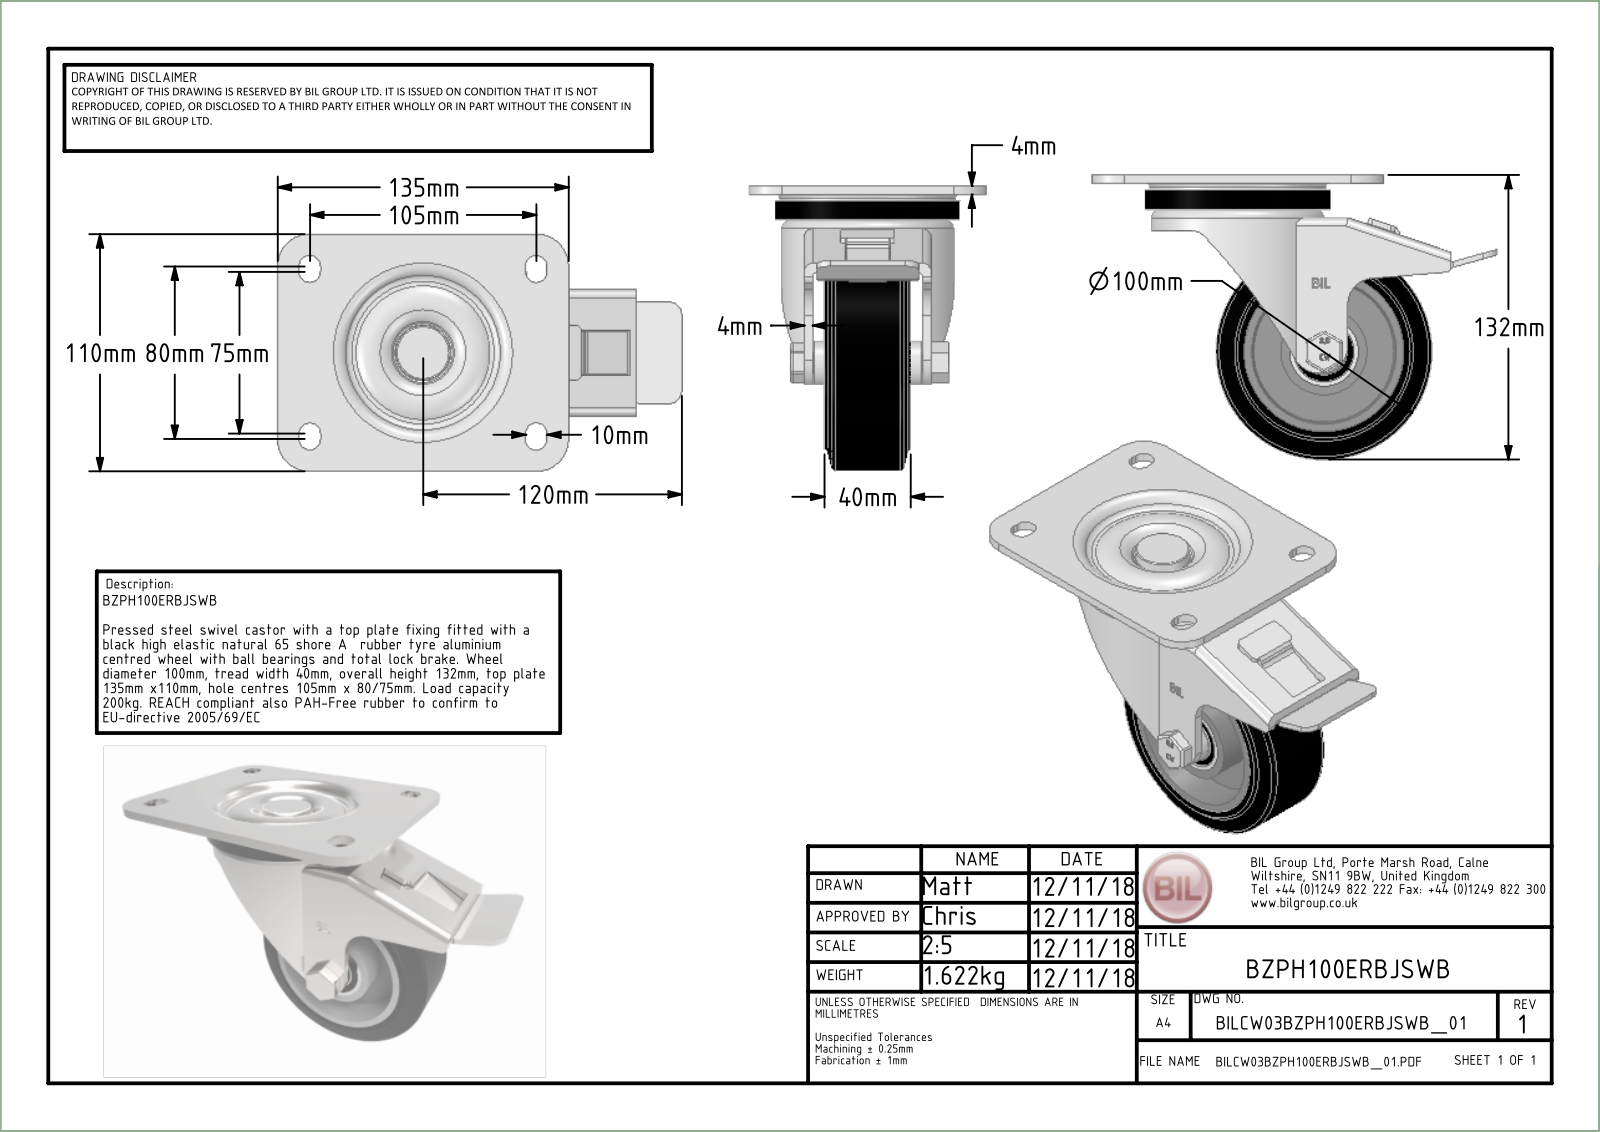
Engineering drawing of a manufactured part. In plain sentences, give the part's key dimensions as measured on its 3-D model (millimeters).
The part is named "BZPH100ERBJSWB v3; BZPH100ASSWB v1; ZINC PLATED, PRESSED STEEL TOP PLATE; ZINC PLATED, PRESSED STEEL FORKS (+8 more)". Its 3-D file was written by "Autodesk Translation Framework v14.4.0.0 (AUTOMOTIVE_DESIGN)". It is 43 solids with 1357 faces: 678 planar, 256 cylindrical and 423 other. Overall it measures 187.5 by 132 by 110 millimeters. Its volume is 401 823 cubic millimeters and its surface area 178 185 square millimeters. Round holes: 1 of diameter 8, 1 of diameter 10, 1 of diameter 10.2, 1 of diameter 10.5, 1 of diameter 12, 1 of diameter 15, 1 of diameter 18, 1 of diameter 20, 1 of diameter 21, 1 of diameter 26, 1 of diameter 27.4, 1 of diameter 28. Round bosses or shafts: 2 of diameter 80, 1 of diameter 100, 1 of diameter 83.5, 1 of diameter 60, 1 of diameter 51, 1 of diameter 40, 1 of diameter 32, 1 of diameter 28.4. Partial cylindrical surfaces (rounded edges, fillets, slot ends): 27 of radius 0.5, 15 of radius 2, 10 of radius 0.75, 10 of radius 4, 8 of radius 5.5, 7 of radius 1.5, 4 of radius 1.25, 4 of radius 3. The main face-to-face distances are 4, 9, 13, 29.5, 25.5, 16, 5.5, 9.5, 8, 49.5.
